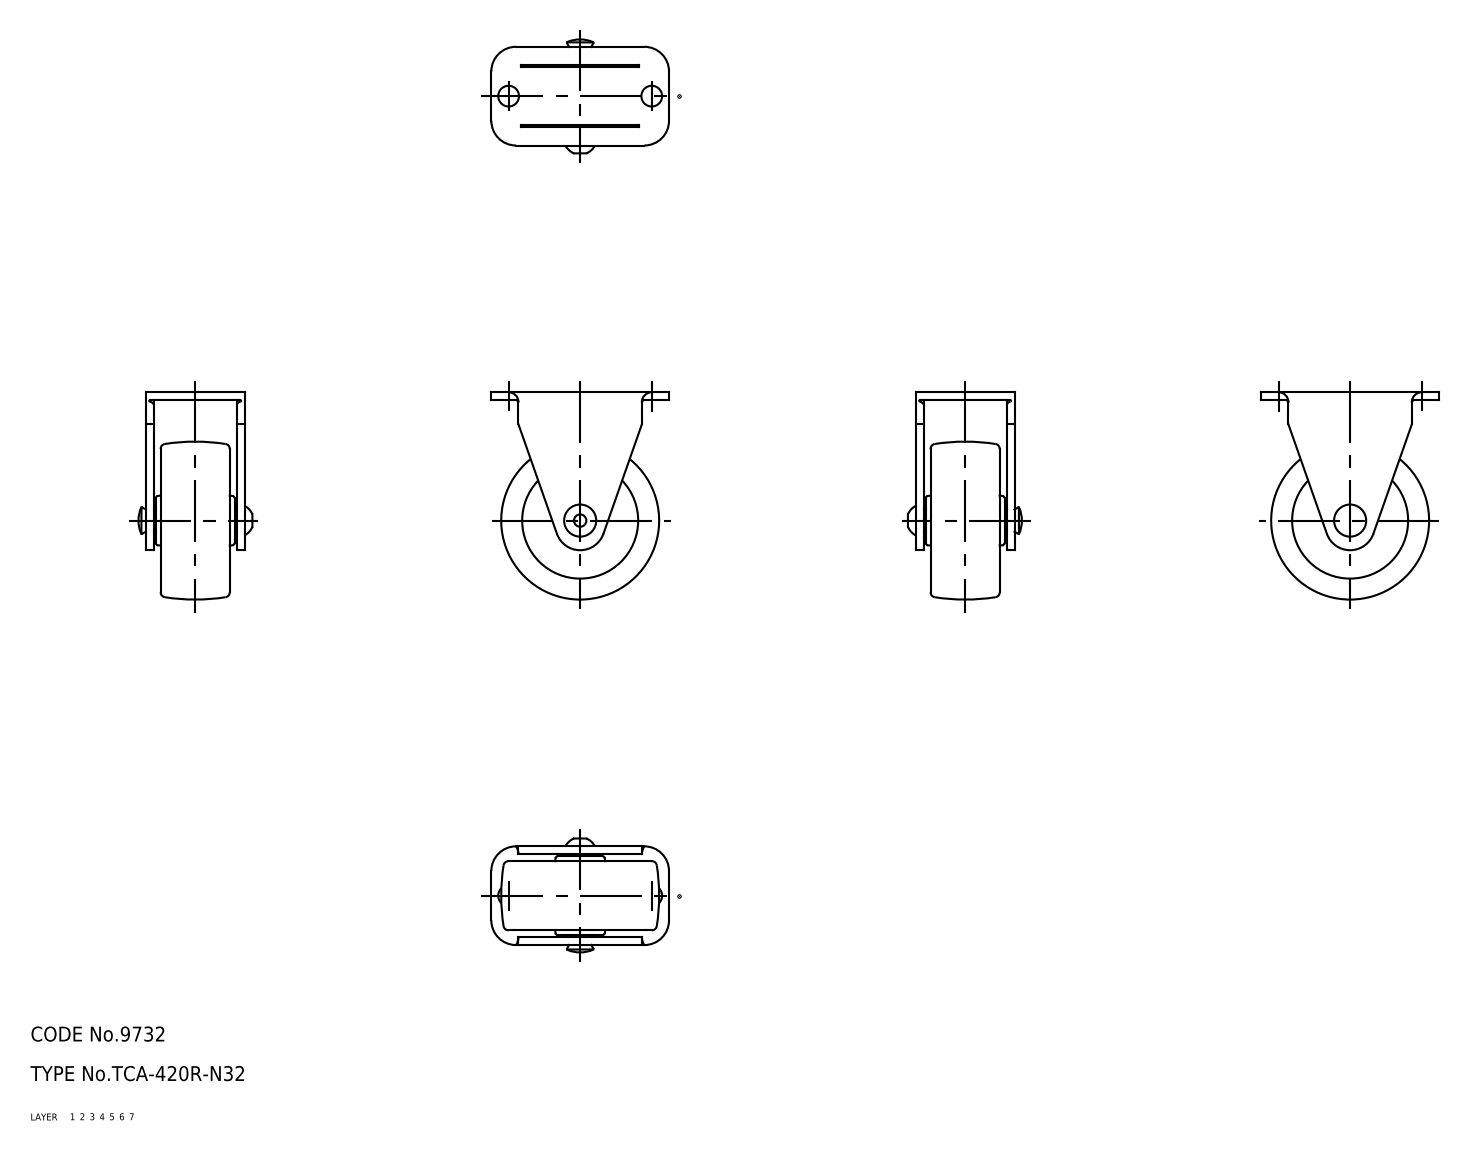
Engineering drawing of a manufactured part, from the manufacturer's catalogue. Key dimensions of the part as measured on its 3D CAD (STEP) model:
Part name (STEP PRODUCT): wheel; axle; No_420_R_N32_2_240_36
STEP written by: CADfix (AUTOMOTIVE_DESIGN)
Units: millimetres
Bodies: 3 solids, 97 faces (0 planar, 0 cylindrical, 97 other)
Overall size (bounding box): 42 × 36 × 23.09
Volume: 12 191 mm³ · Surface area: 7 638 mm²
